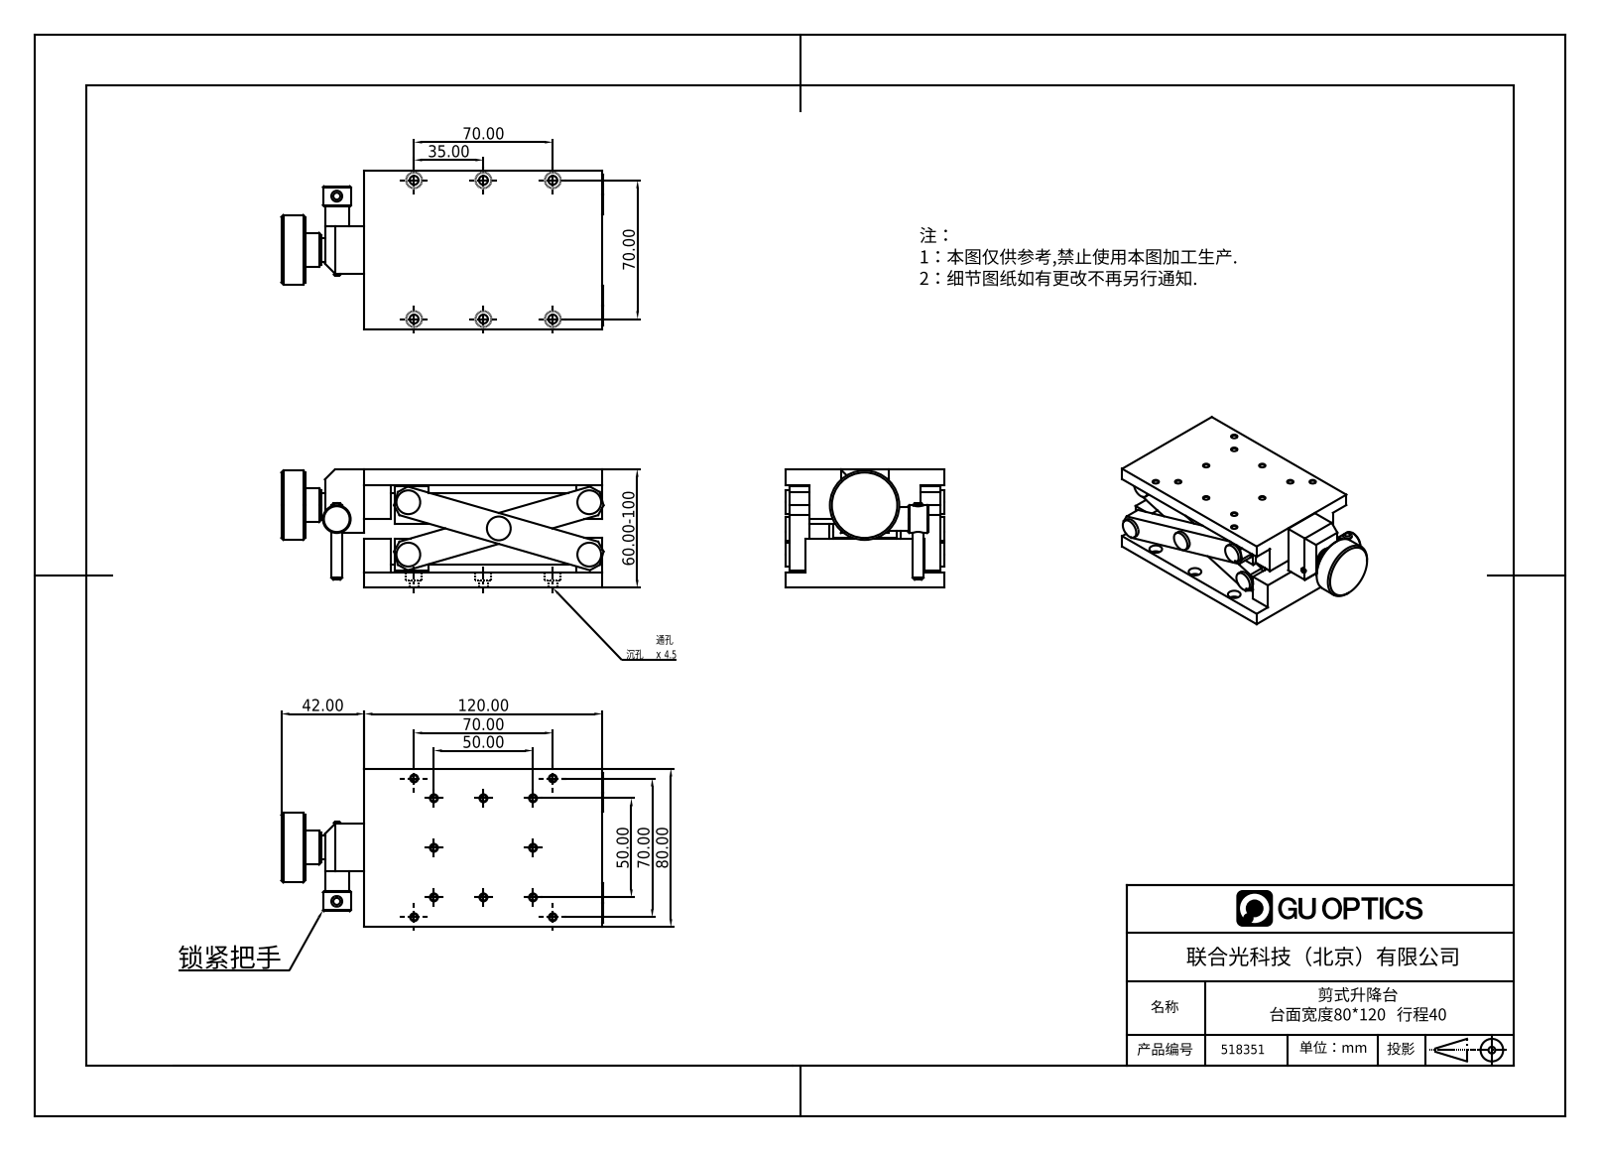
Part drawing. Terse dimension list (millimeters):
name: 518351
written by: SolidWorks 2020 (CONFIG_CONTROL_DESIGN)
unit: mm
bodies: 10 solids, 305 faces (133 planar, 108 cylindrical, 64 other)
size: 162.62 × 80 × 60
volume: 336 372 mm³; area: 100 915 mm²
holes: 12× ⌀3.24, 6× ⌀4.5, 6× ⌀8, 5× ⌀12
bosses: 2× ⌀12, 1× ⌀35, 1× ⌀17, 1× ⌀14, 1× ⌀5.5, 1× ⌀3
face distances: 8, 52, 12, 60, 10, 48, 40, 44, 56, 68
hole spacings: 25, 36.4, 55.9, 60.83, 69.46, 50, 70, 14.14
